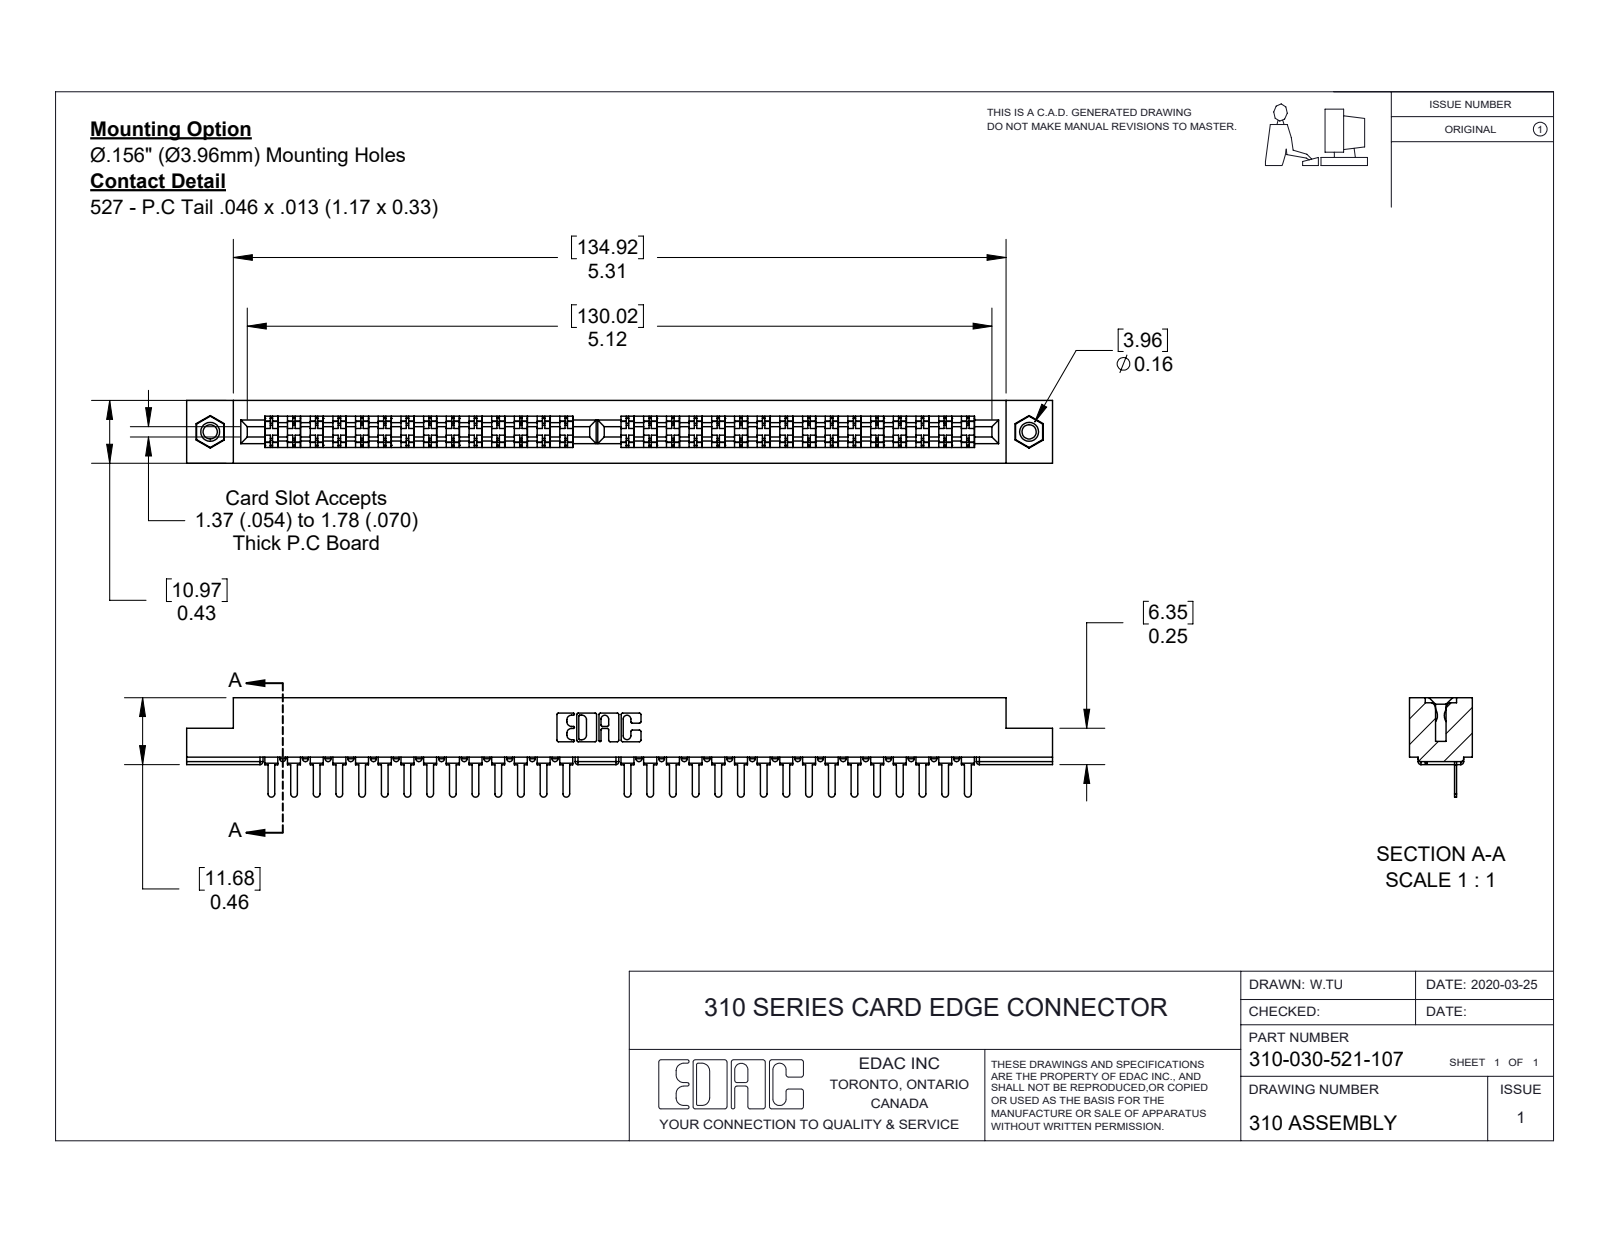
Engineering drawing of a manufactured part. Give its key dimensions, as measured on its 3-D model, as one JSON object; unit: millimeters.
{"part_name": "345-250-001_345-250-005-103; 310-030-521-107; 310 Part_.116 Hex; 307-290-002_521", "step_written_by": "SolidWorks 2016 (CONFIG_CONTROL_DESIGN)", "units": "millimeters", "bodies": {"solids": 33, "faces": 2446, "planar": 1466, "cylindrical": 900, "other": 80}, "overall_size": [151.21, 17.37, 10.97], "volume_mm3": 13090, "surface_area_mm2": 18403, "round_holes": [[2.5, 2], [3.17, 2], [3.96, 2]], "round_bosses_or_shafts": [[3.94, 2]], "partial_cylinders_radius": [[0.51, 98], [0.58, 30], [0.25, 22], [0.17, 6], [0.8, 6], [0.67, 3], [0.31, 2], [0.64, 2]], "face_to_face_distances": [2.76, 8.22, 0.33, 10.98, 5.13, 3.09, 7.89, 5.46, 1.24, 3.89], "hole_center_spacings": [143]}
